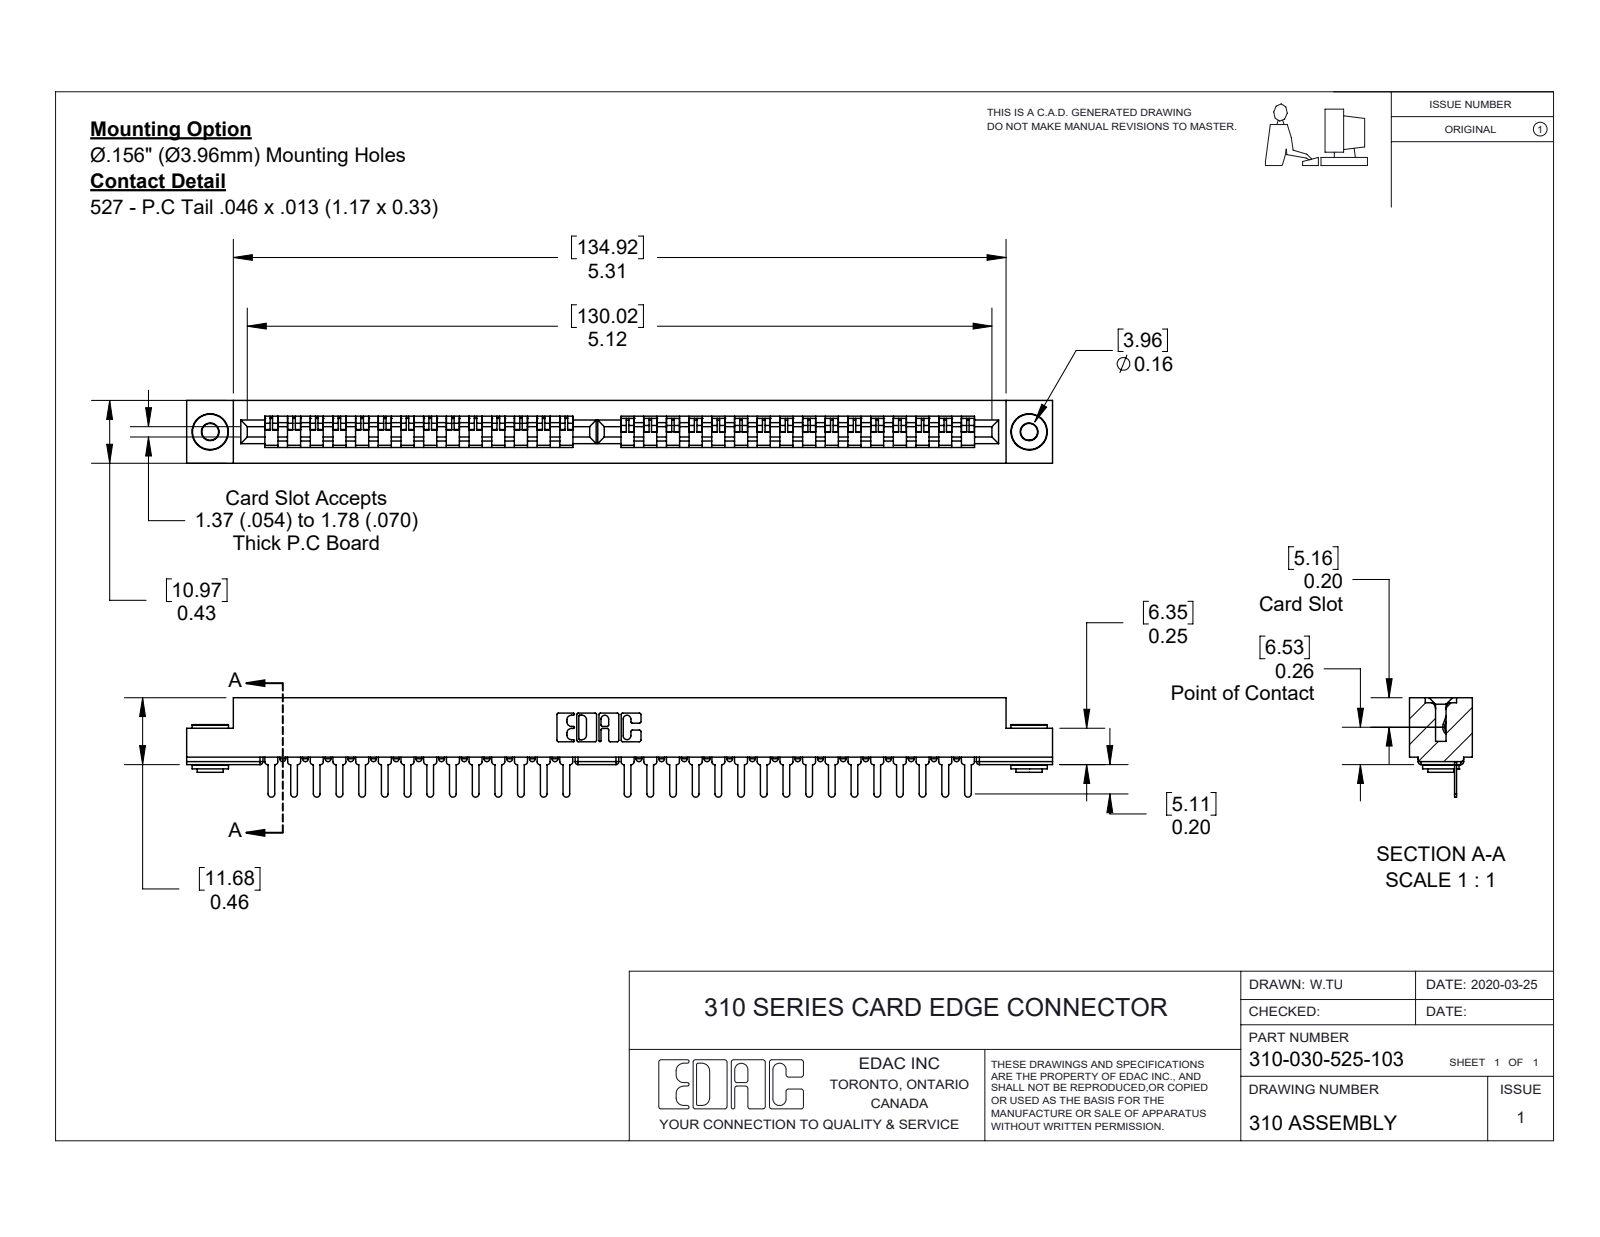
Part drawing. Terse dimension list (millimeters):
name: 307-290-001_525; 310 Part_.116 Hex; 345-250-002_345-250-002-102; 310-030-525-103
written by: SolidWorks 2016 (CONFIG_CONTROL_DESIGN)
unit: mm
bodies: 33 solids, 1898 faces (1218 planar, 608 cylindrical, 72 other)
size: 151.21 × 17.37 × 10.97
volume: 12 647 mm³; area: 15 092 mm²
holes: 2× ⌀2.95, 2× ⌀3.96
bosses: 2× ⌀6.35, 2× ⌀4.57, 2× ⌀3.45
rounds: 158× R0.51, 30× R0.58, 22× R0.25, 6× R0.17, 6× R0.8, 3× R0.67, 2× R0.3, 2× R0.64
face distances: 2.76, 8.22, 10.98, 0.38, 1.82, 0.33, 10.38, 5.46, 6.4, 4.58
hole spacings: 143
